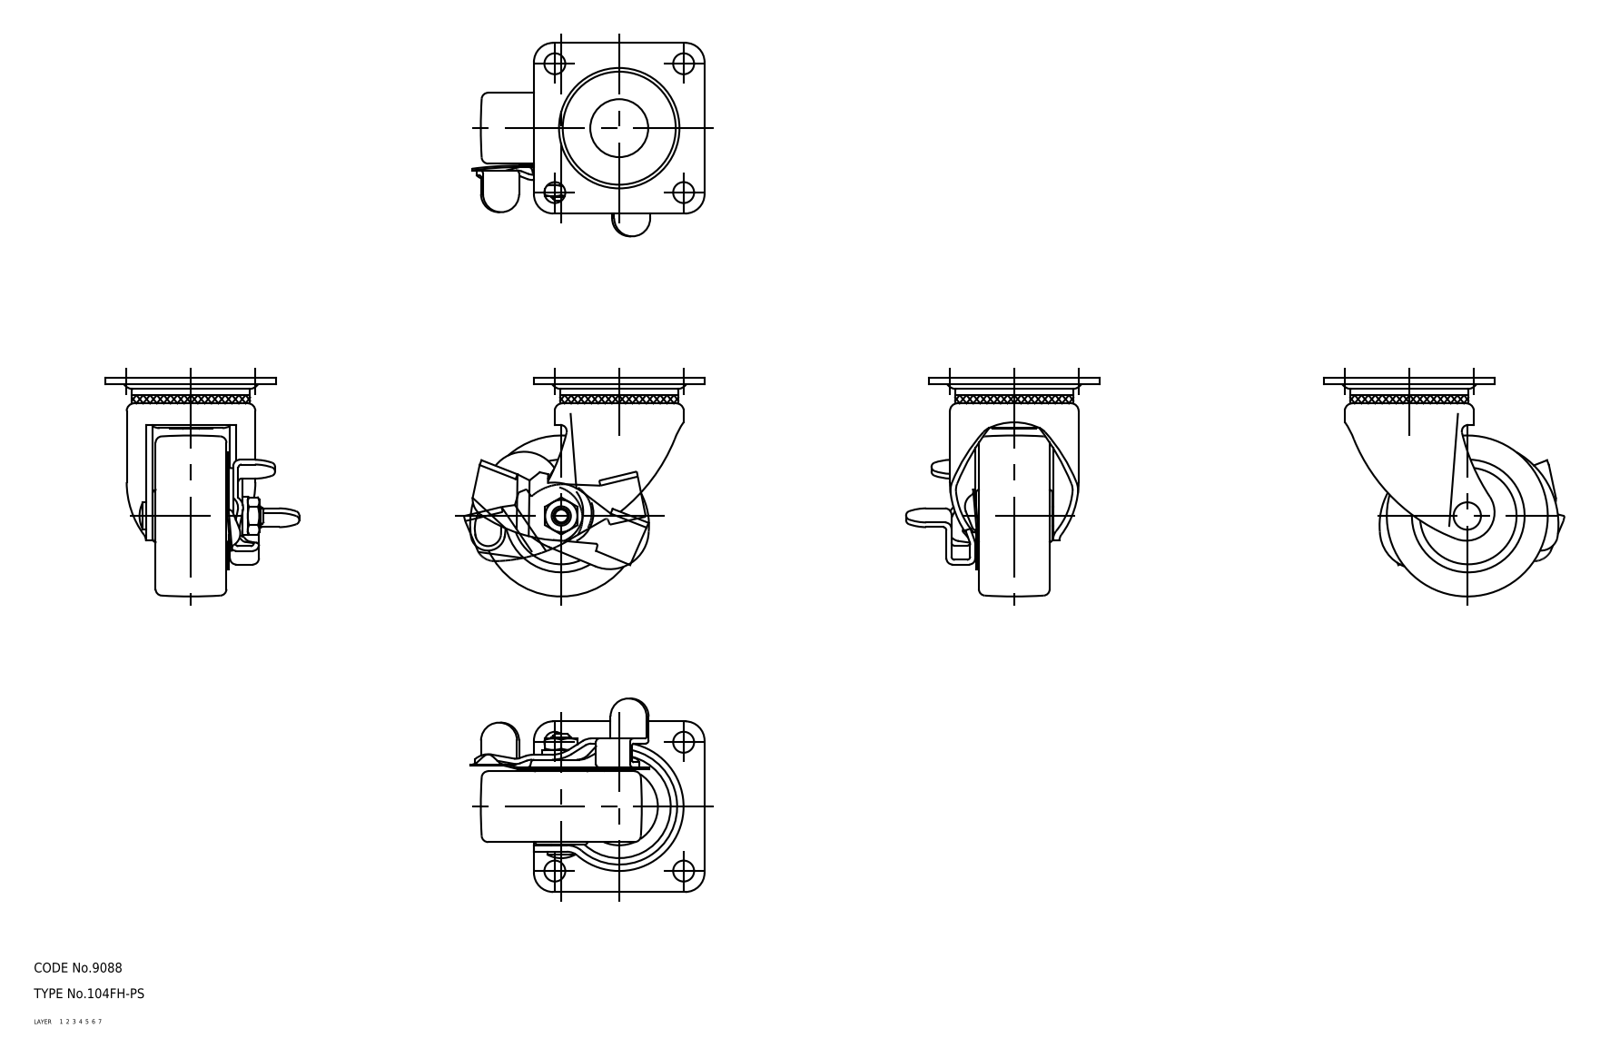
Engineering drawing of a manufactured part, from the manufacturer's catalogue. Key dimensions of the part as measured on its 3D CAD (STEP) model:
Part name (STEP PRODUCT): plate; lever; wheel; mounting plate (+3 more)
STEP written by: CADfix (AUTOMOTIVE_DESIGN)
Units: millimetres
Bodies: 7 solids, 453 faces (0 planar, 0 cylindrical, 453 other)
Overall size (bounding box): 72.81 × 68 × 60.08
Volume: 62 308 mm³ · Surface area: 31 947 mm²
